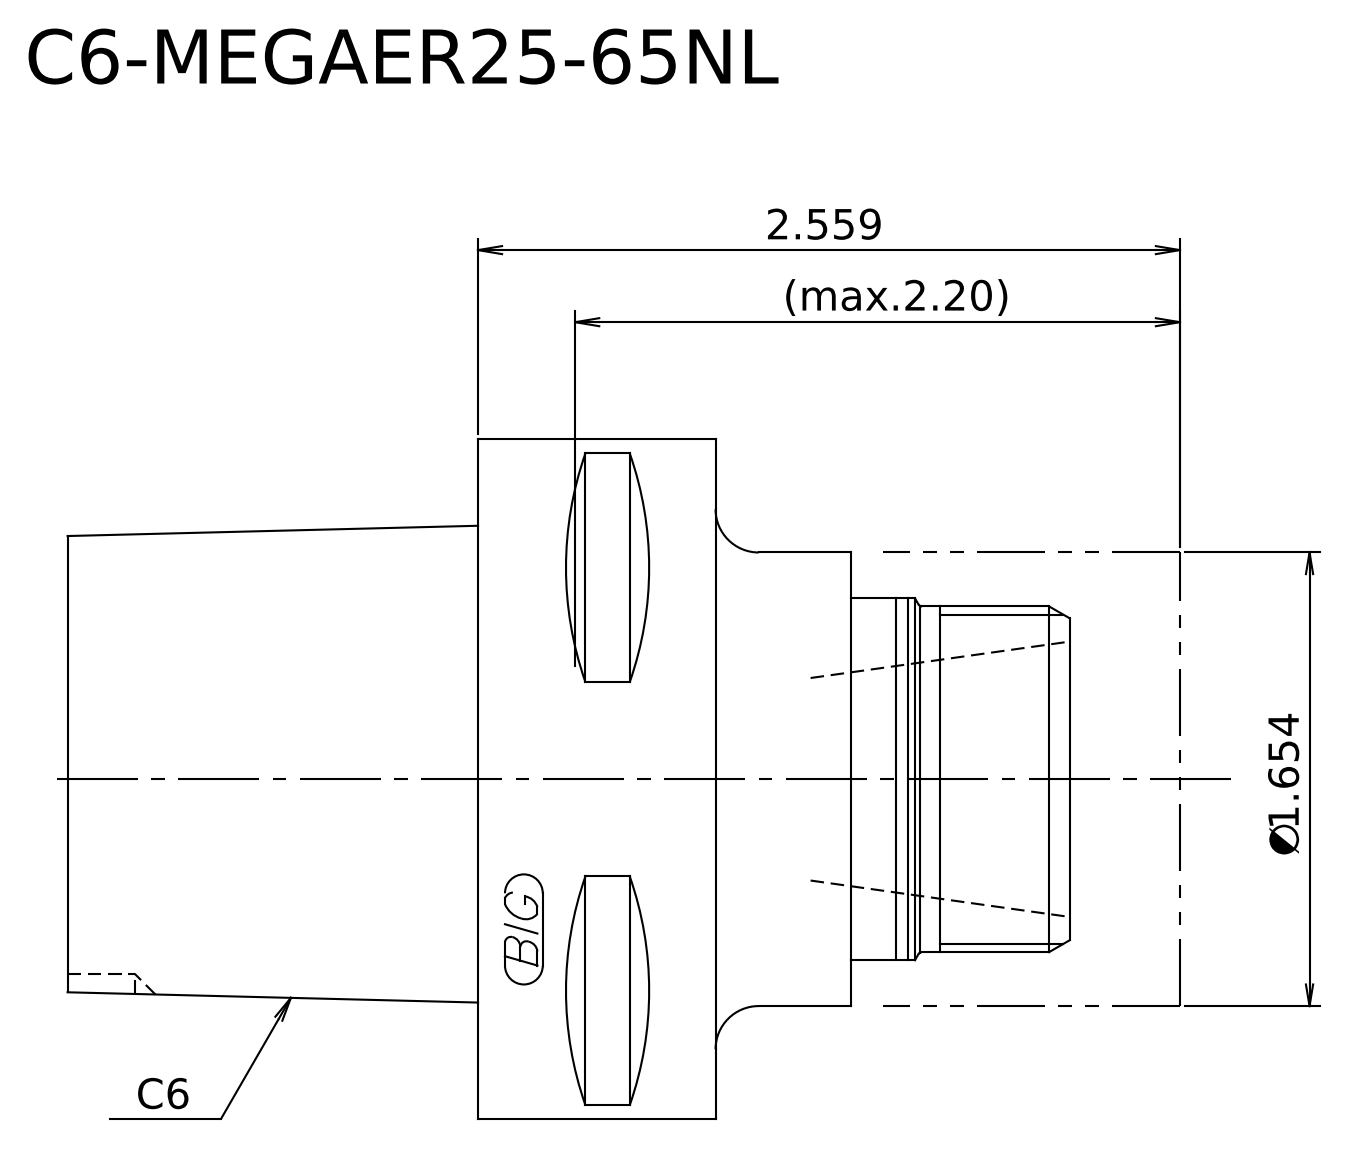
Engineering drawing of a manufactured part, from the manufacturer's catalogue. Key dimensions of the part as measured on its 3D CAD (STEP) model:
STEP written by: Kubotek KeyCreator 2011 V10.0.2 (22737) (automotive_design)
Units: millimetres
Bodies: 2 solids, 18 faces (7 planar, 5 cylindrical, 6 other)
Overall size (bounding box): 103 × 63 × 63
Volume: 196 601 mm³ · Surface area: 25 331 mm²
Round bosses / shafts (diameter × count): ⌀63 ×1, ⌀42 ×1, ⌀33.5 ×1, ⌀32 ×1
Main face-to-face distances: 37.5, 27.5, 65, 103, 75.5, 38, 43, 15.5, 22, 60
